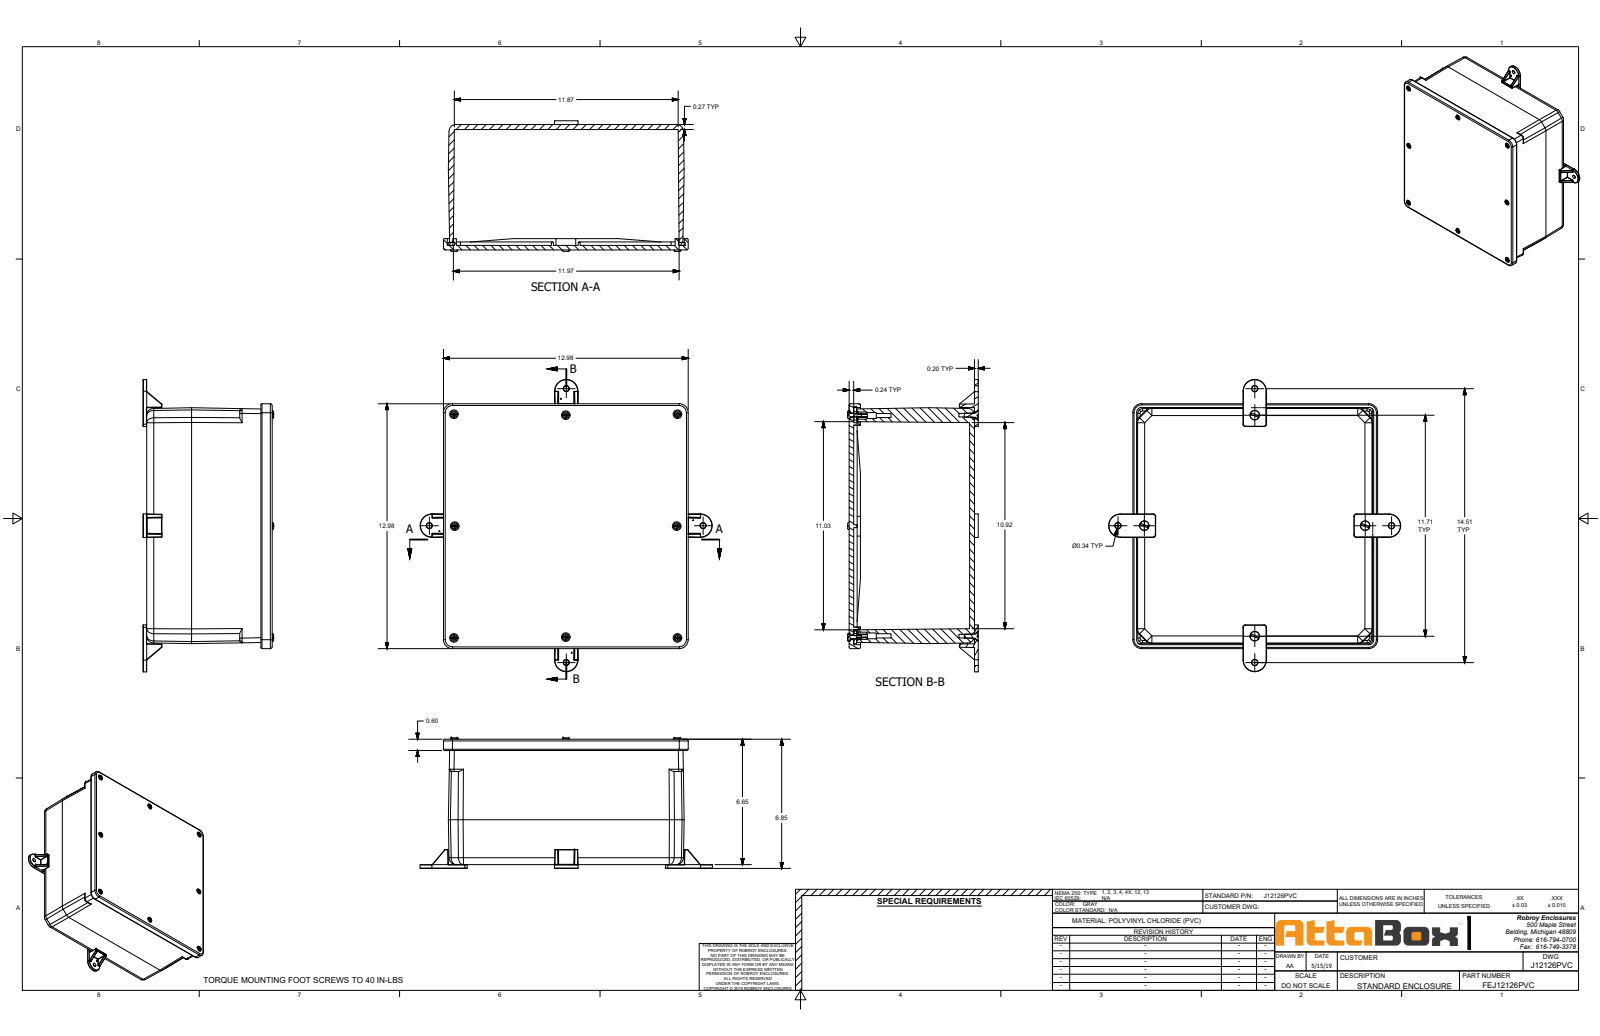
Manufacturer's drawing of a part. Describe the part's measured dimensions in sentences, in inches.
The part is named "J12126PVC". Its 3-D file was written by "SolidWorks 2018 (AUTOMOTIVE_DESIGN)". It is 35 solids with 1505 faces: 717 planar, 528 cylindrical and 260 other. Overall it measures 15.49 by 15.49 by 6.923 inches. Its volume is 175.5 cubic inches and its surface area 1 432 square inches. Round holes: 8 of diameter 0.13, 8 of diameter 0.2, 8 of diameter 0.267, 8 of diameter 0.276, 8 of diameter 0.313, 8 of diameter 0.46, 4 of diameter 0.19, 4 of diameter 0.22, 4 of diameter 0.265, 4 of diameter 0.35, 4 of diameter 0.371, 4 of diameter 0.385. Round bosses or shafts: 8 of diameter 0.354, 8 of diameter 0.187, 8 of diameter 0.177, 7 of diameter 0.325, 4 of diameter 0.224, 1 of diameter 0.325. Partial cylindrical surfaces (rounded edges, fillets, slot ends): 76 of radius 0.02, 48 of radius 0.025, 32 of radius 0.005, 32 of radius 0.03, 24 of radius 0.375, 20 of radius 0.094, 12 of radius 0.125, 12 of radius 0.25. The main face-to-face distances are 0.24, 6.407, 6.647, 0.265, 6.142, 6.382, 12.5, 6.25, 5.985, 0.157. The hole center spacings are 5.9, 5.875, 5.9, 5.925, 11.75, 11.8, 13.135, 13.137.
